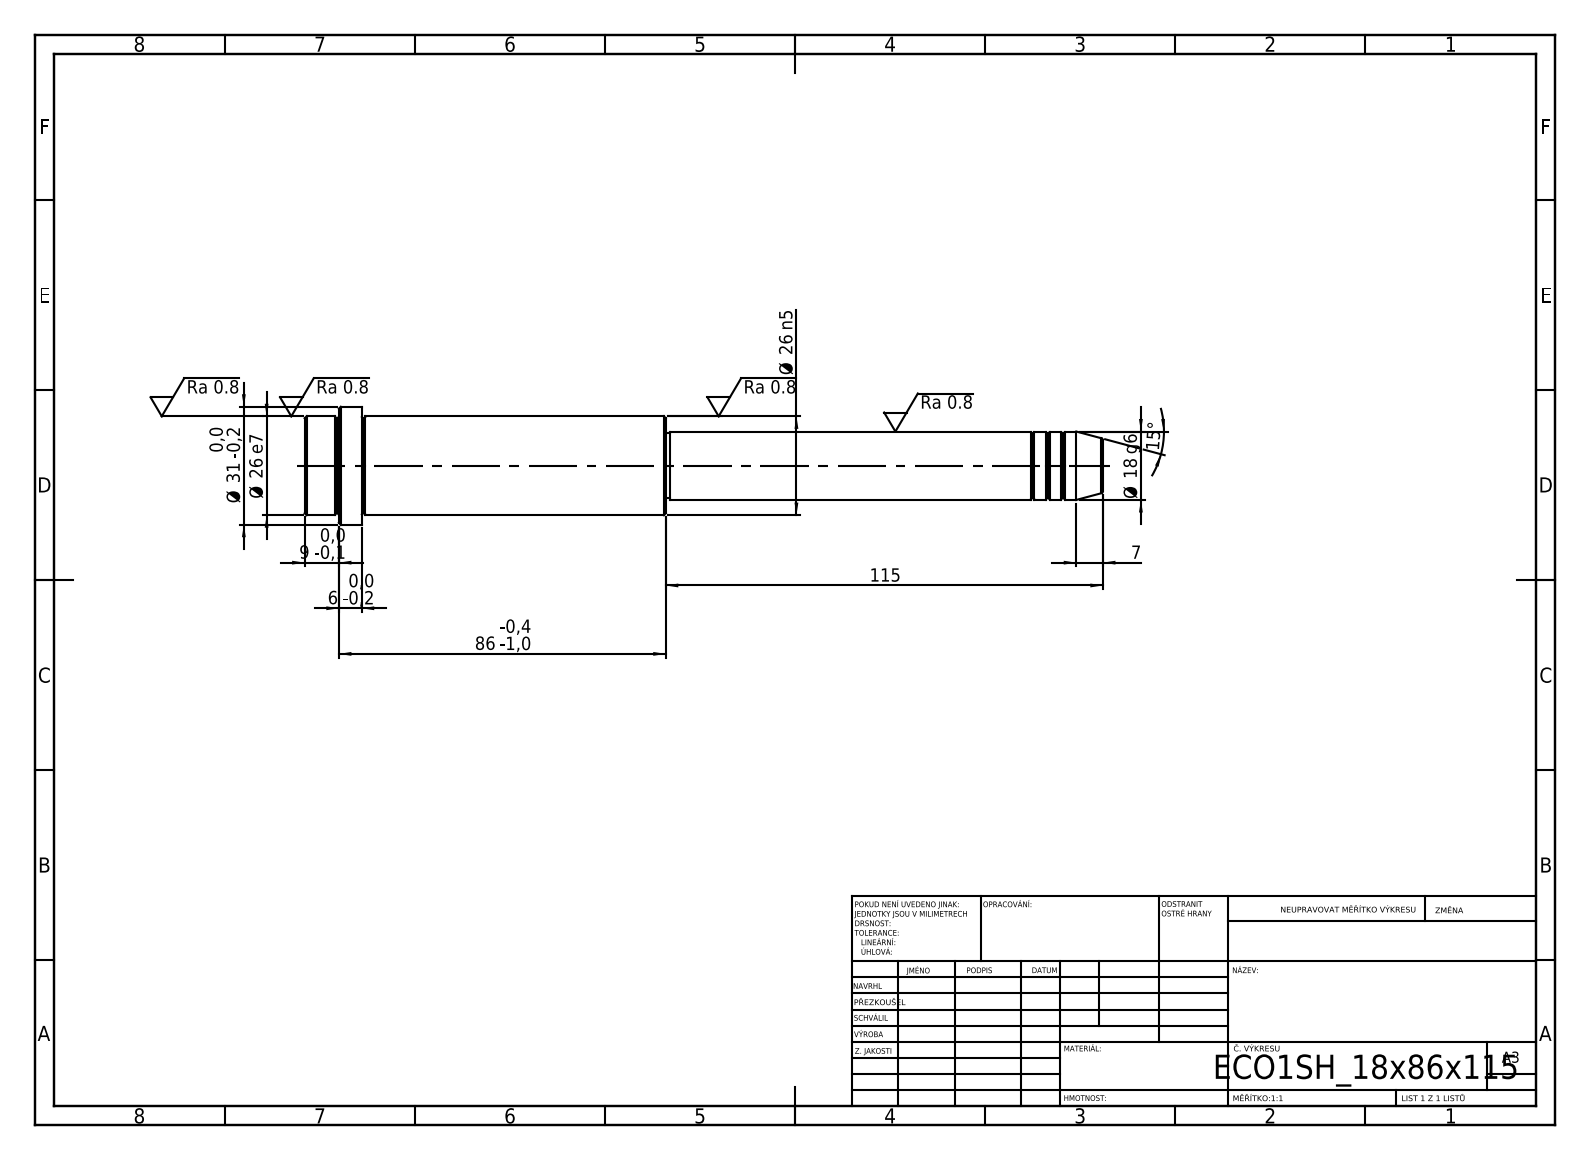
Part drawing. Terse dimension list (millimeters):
written by: SolidWorks 2019 (CONFIG_CONTROL_DESIGN)
unit: mm
bodies: 1 solid, 52 faces (6 planar, 16 cylindrical, 30 other)
size: 210 × 31 × 31
volume: 80 511 mm³; area: 15 887 mm²
bosses: 1× ⌀31, 1× ⌀26, 1× ⌀18, 1× ⌀17
face distances: 95, 80, 15, 86, 6, 9, 115, 195, 201, 210
